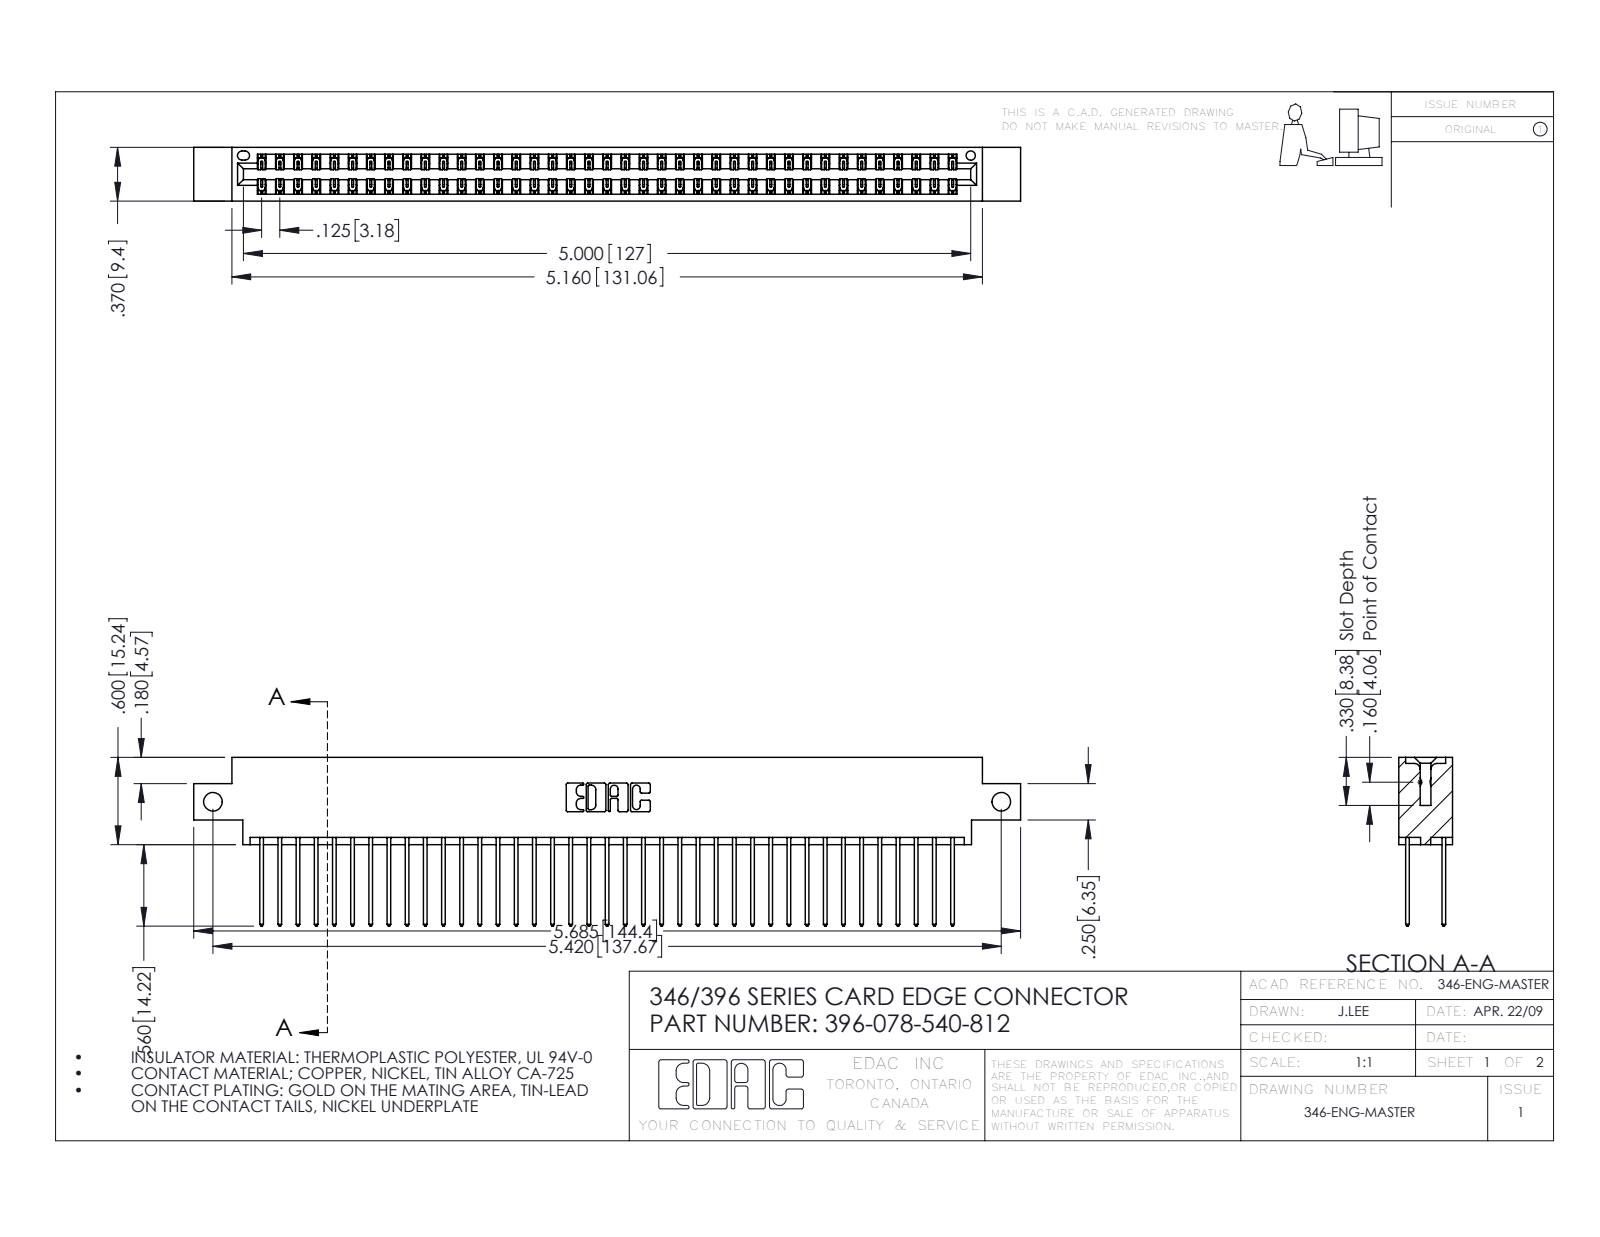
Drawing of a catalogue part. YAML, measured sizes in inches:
part_name: "346 Part_0.170 Offset - Side Mount; 396-078-540-812; 345-292-001_345-293-140"
step_written_by: "SolidWorks 2016 (CONFIG_CONTROL_DESIGN)"
units: inches
bodies: {solids: 79, faces: 4182, planar: 2810, cylindrical: 1372, other: 0}
overall_size: [5.685, 1.16, 0.37]
volume: 0.861
surface_area: 32.23
round_holes:
  - {diameter: 0.128, count: 2}
  - {diameter: 0.064, count: 1}
partial_cylinders:
  - {radius: 0.006, count: 117}
  - {radius: 0.01, count: 78}
  - {radius: 0.01, count: 22}
  - {radius: 0.007, count: 6}
  - {radius: 0.031, count: 6}
  - {radius: 0.026, count: 3}
  - {radius: 0.014, count: 2}
  - {radius: 0.022, count: 2}
face_to_face_distances: [0.048, 0.322, 0.25, 0.072, 0.298, 0.025, 0.37, 0.275, 0.148, 0.222]
hole_center_spacings: [5.42]
